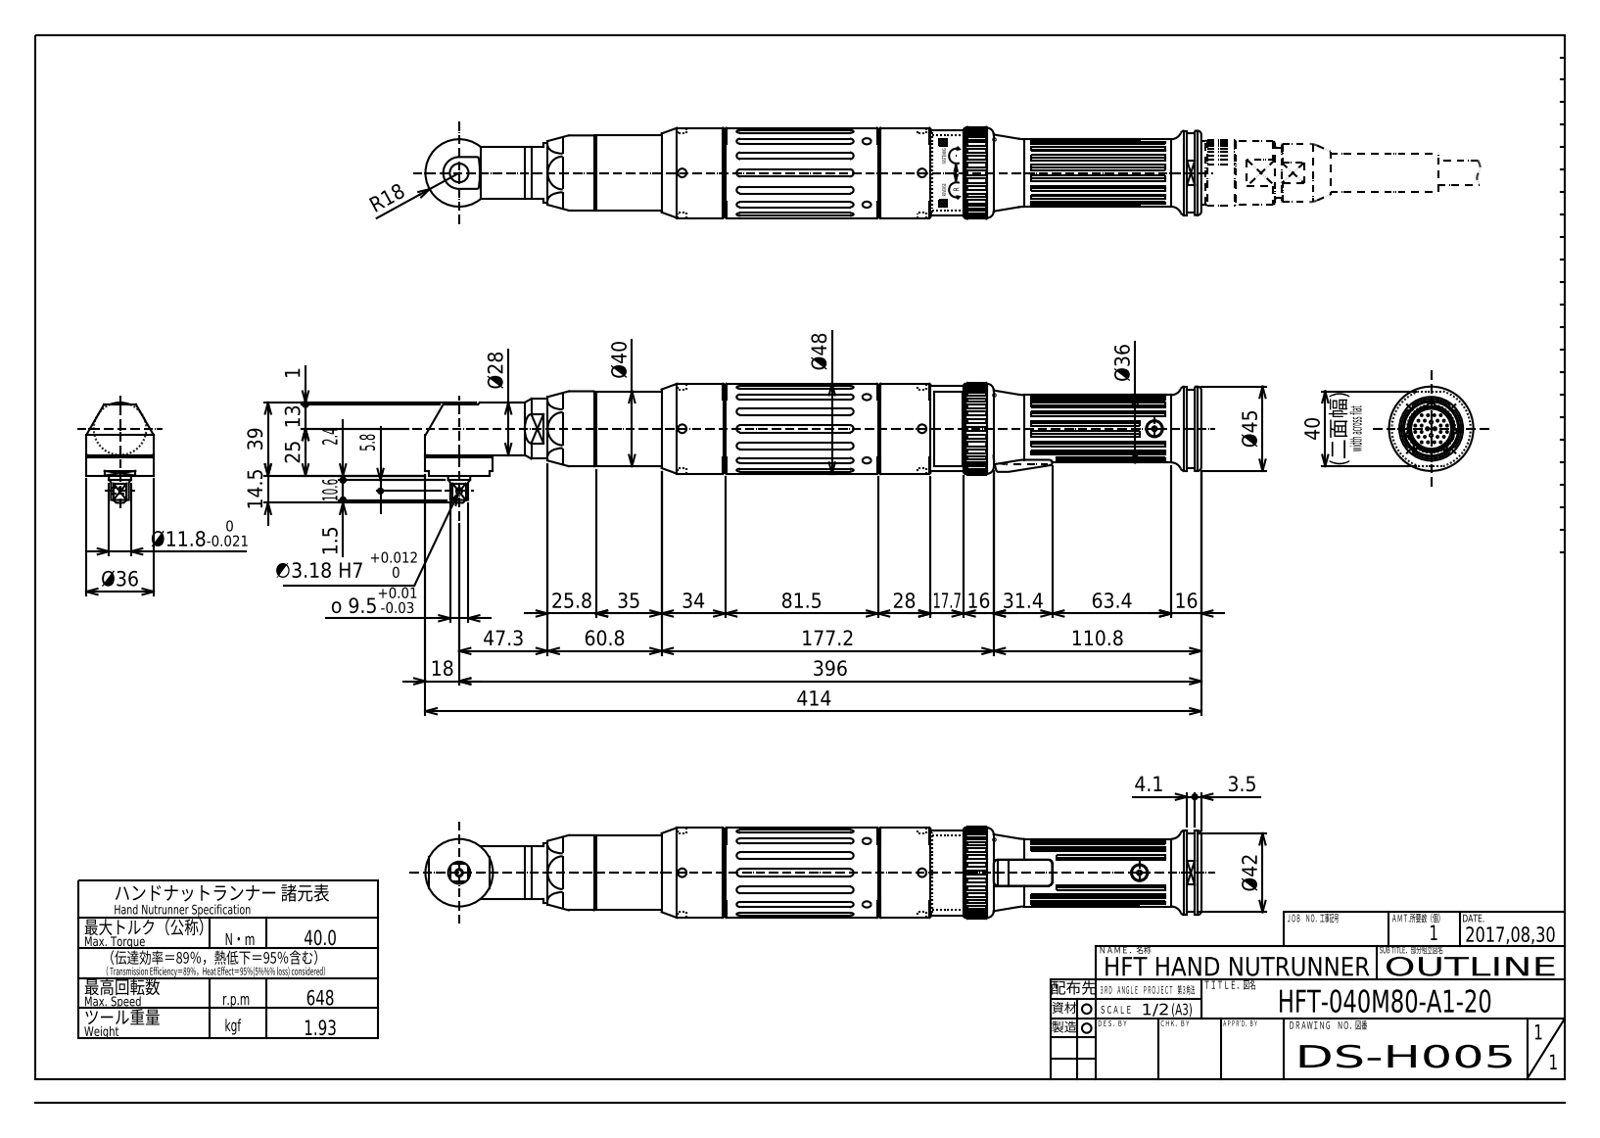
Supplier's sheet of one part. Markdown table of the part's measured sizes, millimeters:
| quantity | value |
| --- | --- |
| part name | HFT-040M80-A1-20(DS-H005)_OUTLINE |
| STEP written by | Autodesk Inventor 2017 (AUTOMOTIVE_DESIGN) |
| units | millimeters |
| bodies | 1 solid, 976 faces (535 planar, 288 cylindrical, 153 other) |
| overall size | 414 × 63.98 × 49 |
| round holes (diameter × count) | 4.6 × 6, 9 × 2, 1.5 × 1, 3 × 1, 3.18 × 1, 4.5 × 1, 6 × 1, 6.8 × 1, 11 × 1, 13.2 × 1, 14.9 × 1, 22.6 × 1 |
| round bosses / shafts (diameter × count) | 1 × 24, 1.6 × 4, 36 × 2, 8 × 2, 4 × 2, 48 × 1, 46 × 1, 45.5 × 1 |
| partial cylindrical surfaces (radius × count) | 0.1 × 36, 1.5 × 36, 2.5 × 23, 0.33 × 18, 0.5 × 8, 1 × 4, 3 × 4, 0.3 × 2 |
| main face-to-face distances | 34.96, 3.5, 8.5, 28, 34, 121.3, 31.48, 3.48, 1.5, 1 |
| hole center spacings | 128, 11, 33.18, 46.3, 57.3, 58.7, 69.7, 116 |
